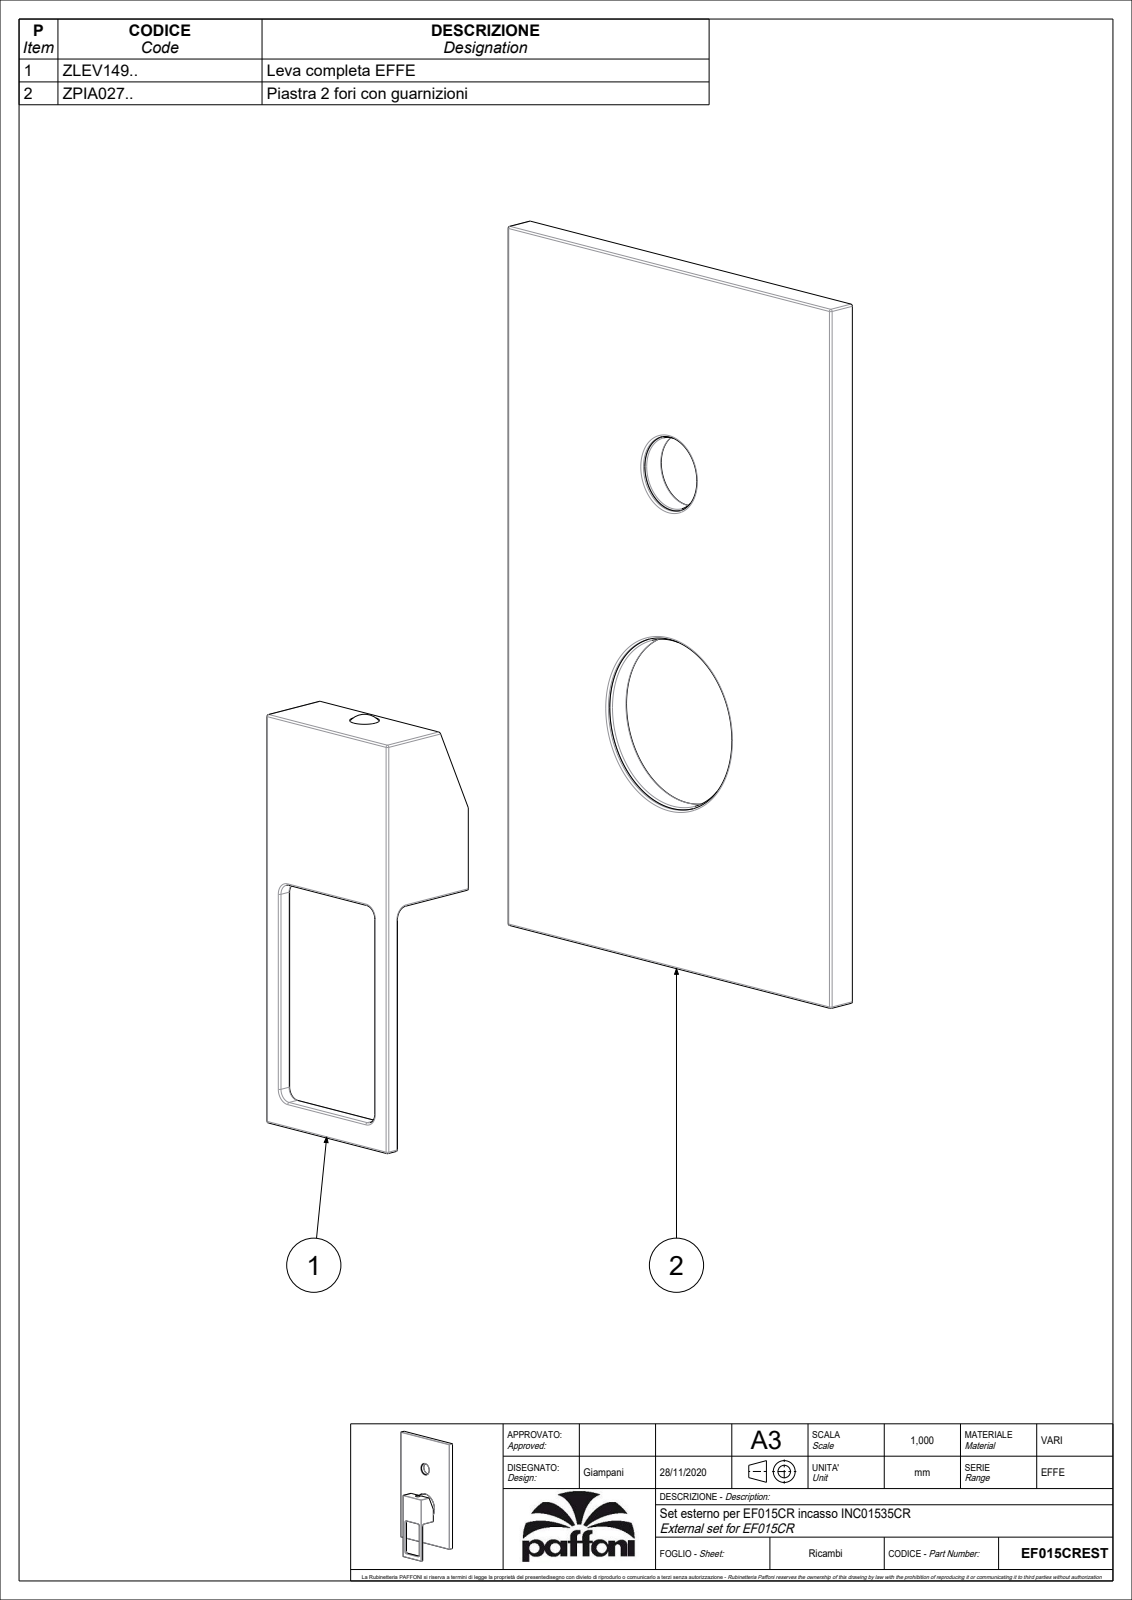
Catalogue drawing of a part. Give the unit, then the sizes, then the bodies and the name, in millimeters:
Units: millimetres
Overall size (bounding box): 212.5 × 120 × 40
Round holes (diameter × count): ⌀3 ×1, ⌀4.5 ×1, ⌀5.5 ×1, ⌀7.8 ×1, ⌀19.2 ×1, ⌀20 ×1, ⌀23.2 ×1, ⌀45 ×1, ⌀46 ×1
Round bosses / shafts (diameter × count): ⌀51 ×1, ⌀49 ×1, ⌀25 ×1, ⌀23 ×1, ⌀7.6 ×1, ⌀5 ×1
Partial cylindrical surfaces — rounded edges, fillets, slot ends (radius × count): R0.5 ×28, R1 ×8, R3 ×5, R4 ×1
Main face-to-face distances: 7.5, 2.5, 5, 0.5, 82.5, 37.5, 32, 39.5, 34.5, 45
Hole centre spacings: 68
Volume: 131 059 mm³ · Surface area: 71 846 mm²
Bodies: 2 solids, 211 faces (78 planar, 81 cylindrical, 52 other)
Part name (STEP PRODUCT): EF015CREST
STEP written by: CREO PARAMETRIC BY PTC INC, 2020044 (CONFIG_CONTROL_DESIGN)
